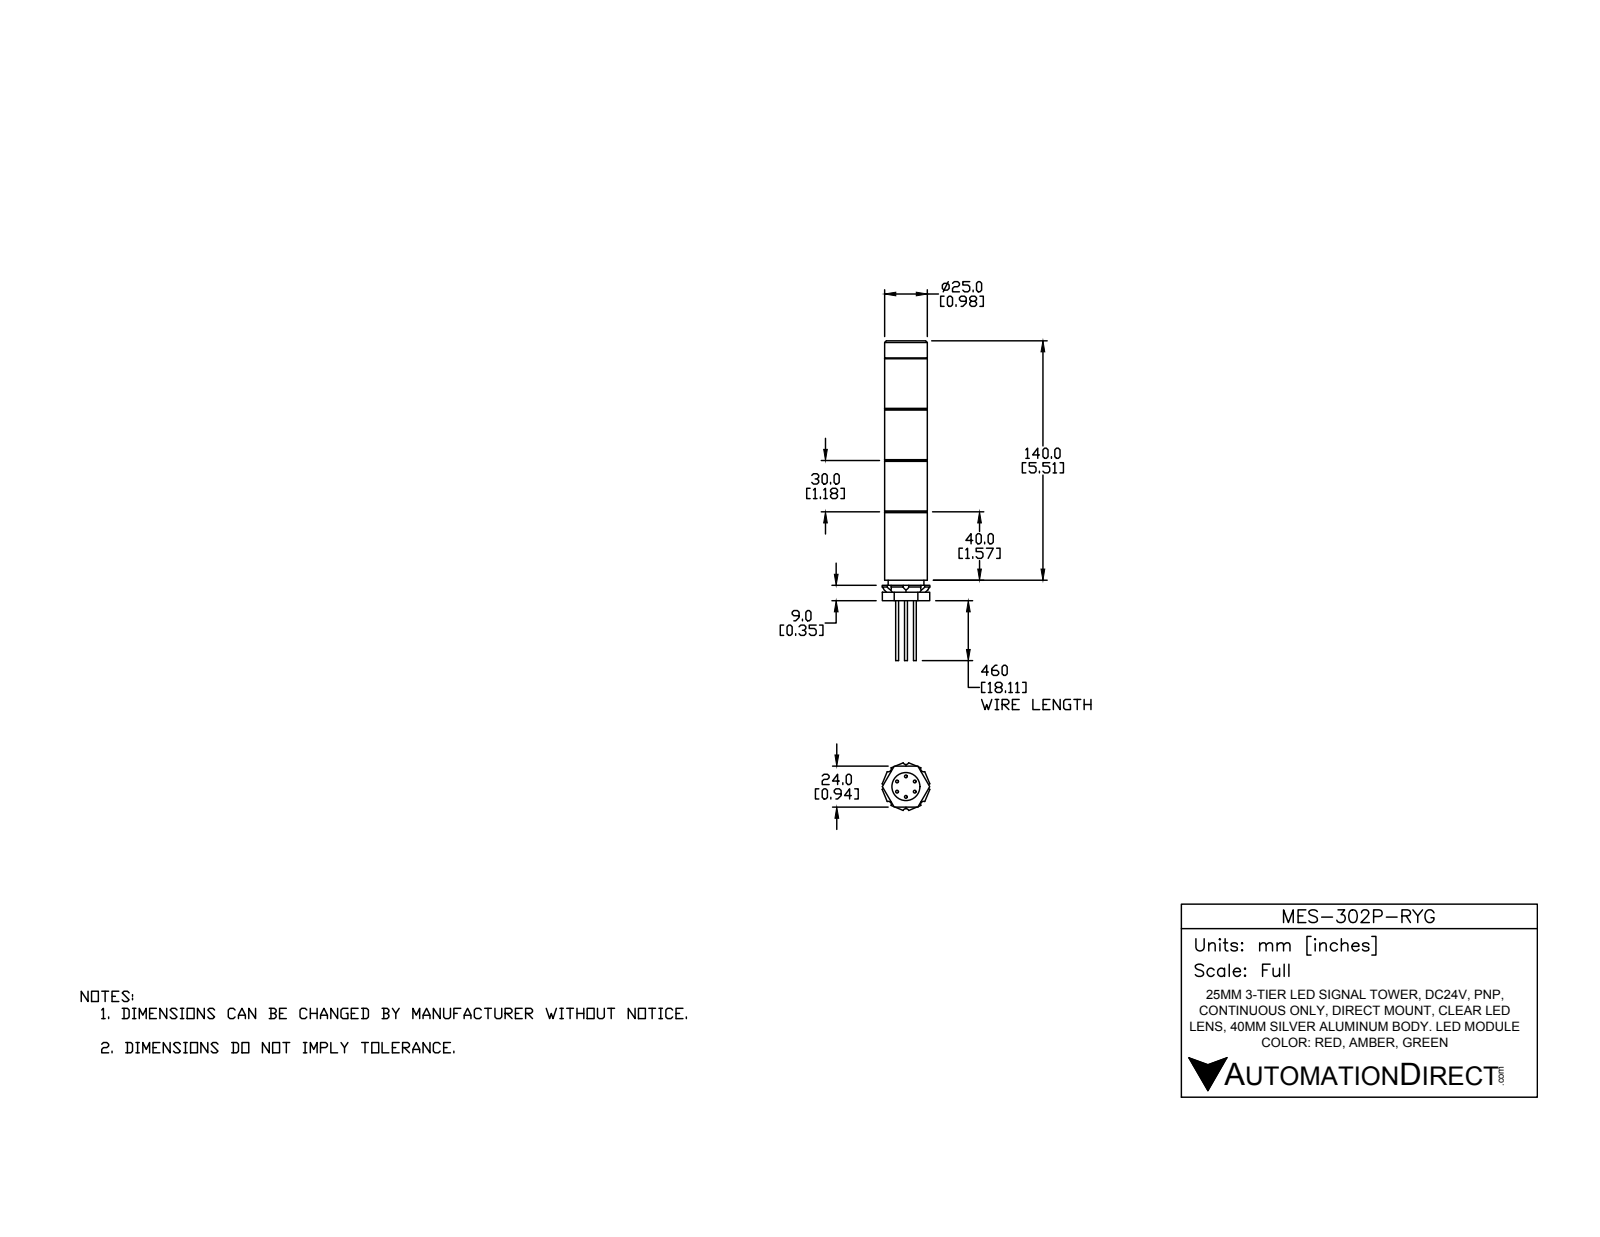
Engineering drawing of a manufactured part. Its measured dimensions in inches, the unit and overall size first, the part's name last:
Units: inches
Overall size (bounding box): 7.362 × 1.098 × 1.098
Round holes (diameter × count): ⌀0.126 ×1, ⌀0.303 ×1, ⌀0.646 ×1, ⌀0.709 ×1, ⌀0.815 ×1, ⌀0.827 ×1
Round bosses / shafts (diameter × count): ⌀0.067 ×6, ⌀0.984 ×1, ⌀0.823 ×1, ⌀0.63 ×1, ⌀0.197 ×1
Partial cylindrical surfaces — rounded edges, fillets, slot ends (radius × count): R0.069 ×8
Main face-to-face distances: 1.181, 2.362, 3.543, 1.575, 0.276, 4.213, 2.756, 3.937, 1.457, 2.638
Volume: 3.849 in³ · Surface area: 39.17 in²
Bodies: 14 solids, 148 faces (75 planar, 51 cylindrical, 22 other)
Part name (STEP PRODUCT): MES-302P-RYG
STEP written by: SolidWorks 2016 (AUTOMOTIVE_DESIGN)
